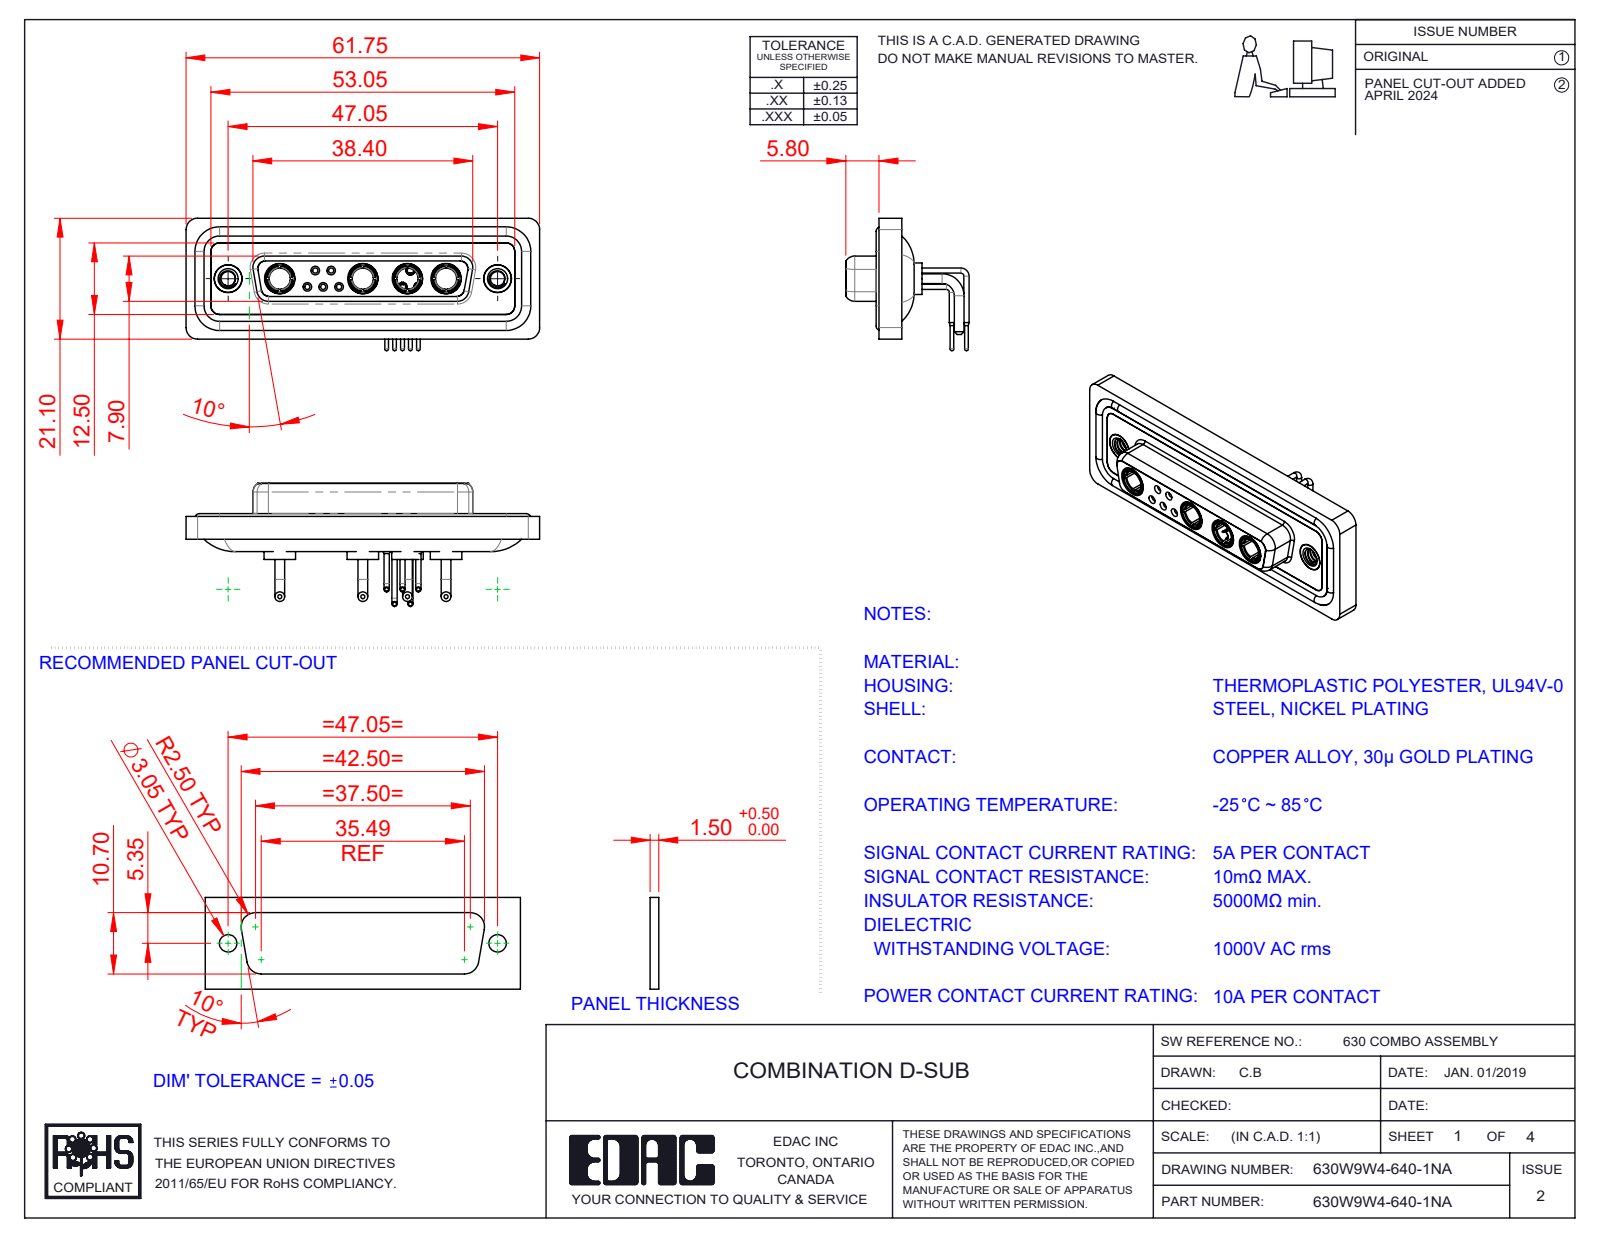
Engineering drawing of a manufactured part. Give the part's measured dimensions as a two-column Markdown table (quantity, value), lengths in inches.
| quantity | value |
| --- | --- |
| part name | 630Combo Housing_9W4; 630Combo Contact Row 1_50 Contacts; 630Combo Contact Row 2_50 Contacts; 630W9W4-640-1NA (+5 more) |
| STEP written by | SolidWorks 2023 (CONFIG_CONTROL_DESIGN) |
| units | inches |
| bodies | 20 solids, 957 faces (296 planar, 401 cylindrical, 260 other) |
| overall size | 2.431 × 0.91 × 0.848 |
| volume | 0.501 in³ |
| surface area | 21.46 in² |
| round holes (diameter × count) | 0.191 × 6, 0.035 × 5, 0.043 × 5, 0.059 × 5, 0.079 × 5, 0.146 × 4, 0.209 × 4, 0.063 × 3, 0.067 × 2, 0.098 × 2, 0.157 × 2, 0.159 × 2 |
| round bosses / shafts (diameter × count) | 0.035 × 10, 0.063 × 9, 0.067 × 8, 0.079 × 5, 0.059 × 5, 0.026 × 5, 0.217 × 4, 0.205 × 4 |
| partial cylindrical surfaces (radius × count) | 0.059 × 18, 0.079 × 18, 0.053 × 8, 0.063 × 8, 0.01 × 4, 0.02 × 4, 0.024 × 4, 0.026 × 4 |
| main face-to-face distances | 0.016, 0.071, 0.161, 0.043, 0.059, 0.063, 0.098, 0.122, 0.146, 0.055 |
| hole center spacings | 0.124, 0.109, 0.198, 0.545, 0.436, 0.504, 0.61, 0.218 |
